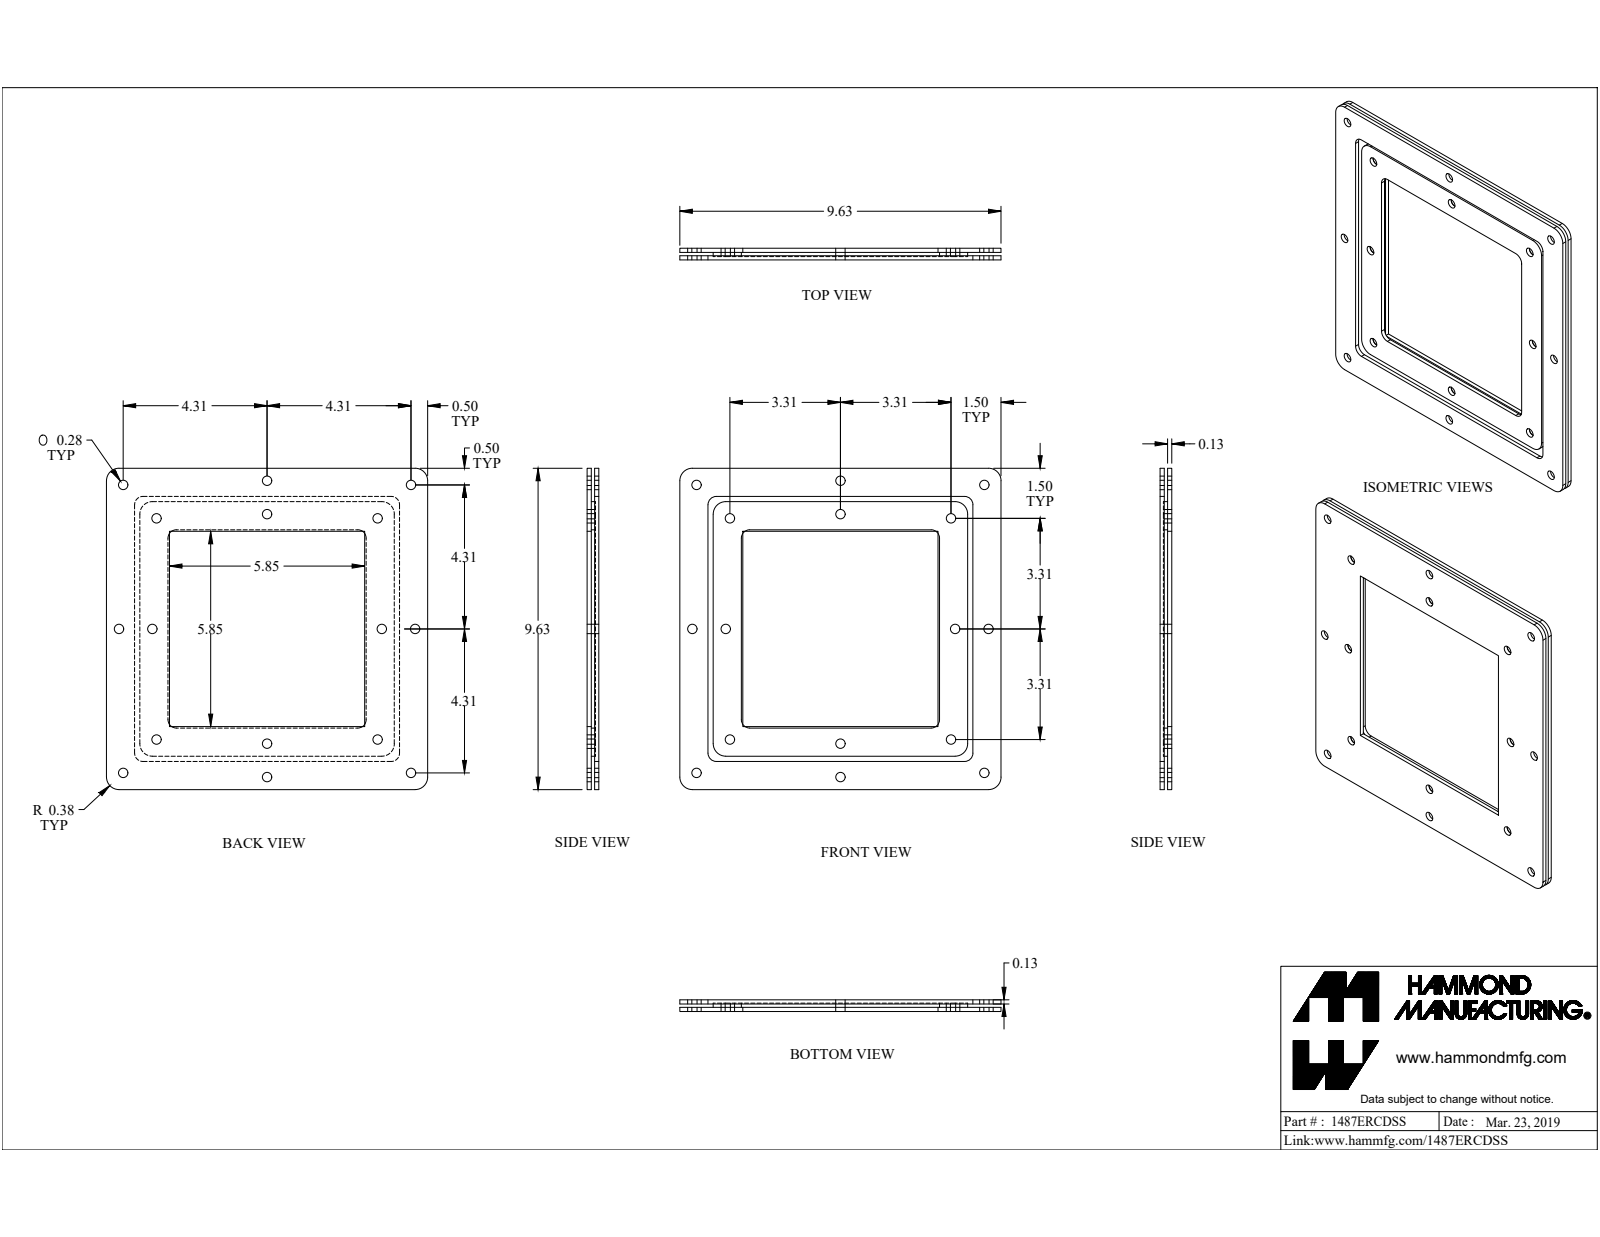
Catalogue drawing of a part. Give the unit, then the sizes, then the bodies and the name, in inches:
Units: inches
Overall size (bounding box): 9.625 × 9.625 × 0.971
Round holes (diameter × count): ⌀0.281 ×16, ⌀0.196 ×2, ⌀0.258 ×2, ⌀0.35 ×2
Round bosses / shafts (diameter × count): ⌀0.5 ×2, ⌀0.25 ×2
Partial cylindrical surfaces — rounded edges, fillets, slot ends (radius × count): R0.02 ×12, R0.25 ×8, R0.375 ×8
Main face-to-face distances: 0.125, 0.125, 0.1, 0.225, 0.225, 0.35, 0.025, 0.25, 0.843, 1
Hole centre spacings: 3.315, 3.498, 4.315, 4.4, 5.613, 7.519, 7.691, 8.428
Volume: 13.76 in³ · Surface area: 248.4 in²
Bodies: 9 solids, 256 faces (144 planar, 96 cylindrical, 16 other)
Part name (STEP PRODUCT): 1487ERCDSS
STEP written by: SolidWorks 2019 (CONFIG_CONTROL_DESIGN)
